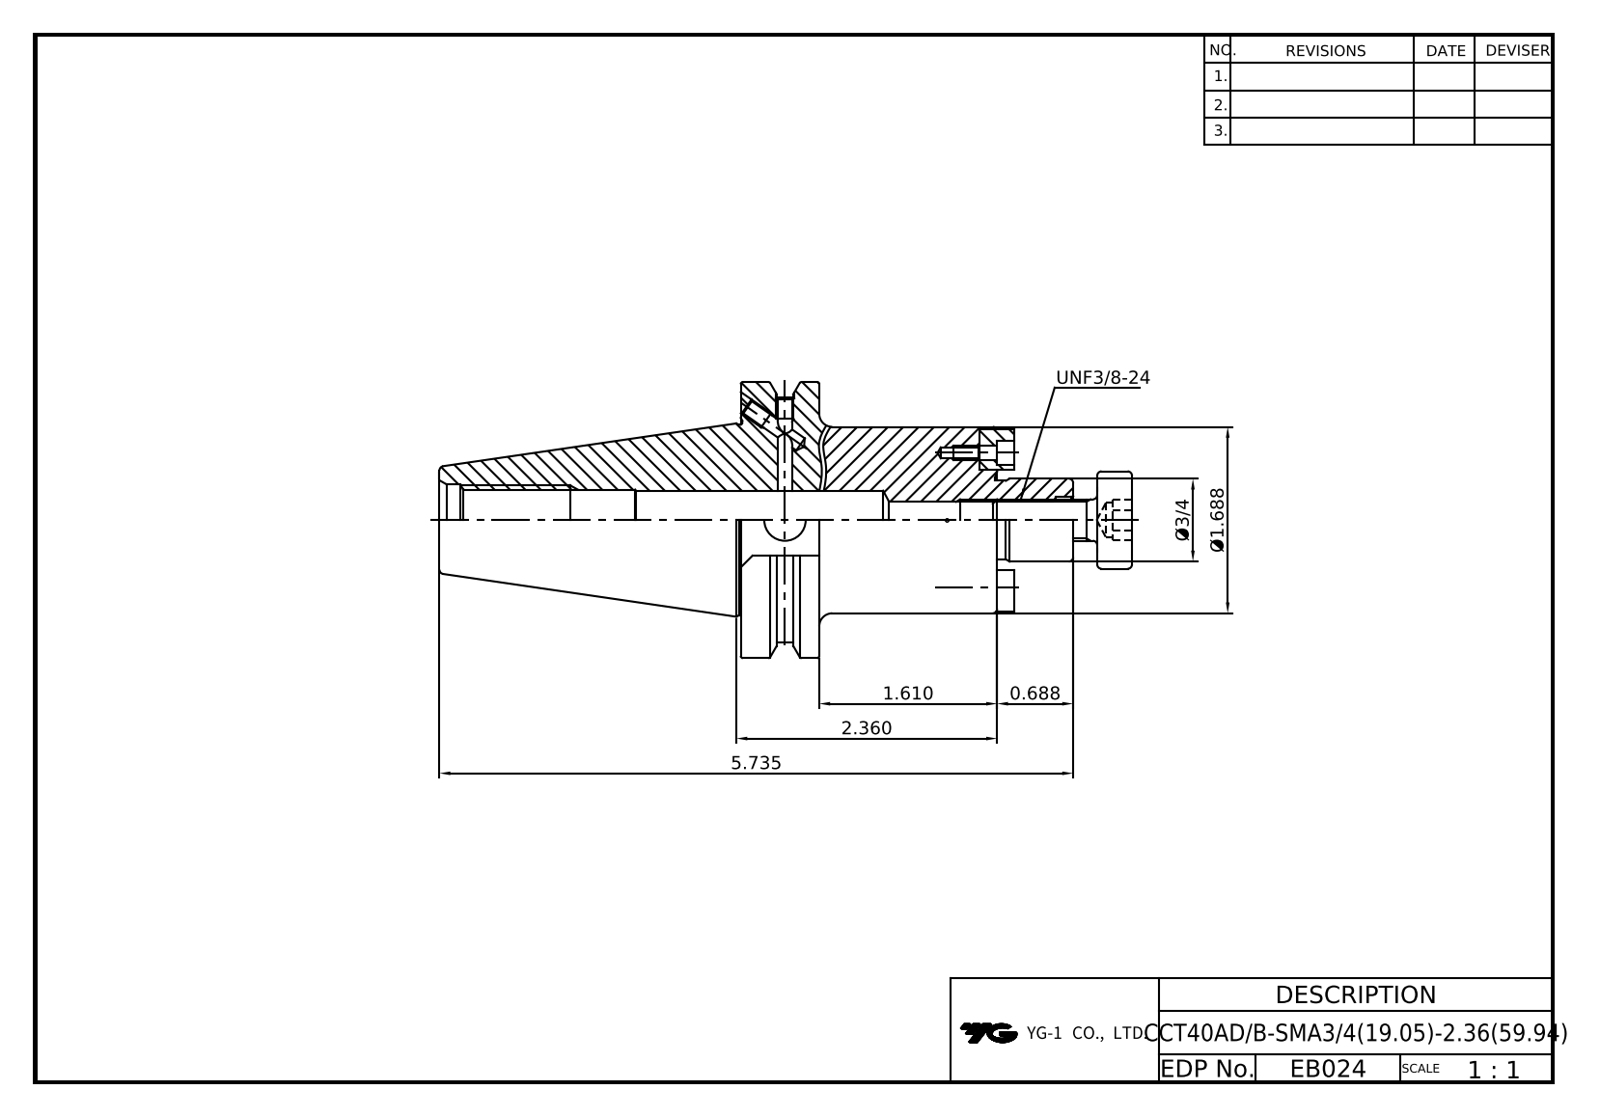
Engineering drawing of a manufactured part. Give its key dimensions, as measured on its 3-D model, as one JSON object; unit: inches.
{"part_name": "LO-CCT40ADB-SMA19.05-59.944; DRIVE KEY-7.93x7.93x9.5; HEX'' WRENCH BOLT-UNC#5-40x5_16L; COLLAR BOLT-UNF3_8-24x24L", "step_written_by": "Autodesk Inventor 2022 (AUTOMOTIVE_DESIGN)", "units": "inches", "bodies": {"solids": 6, "faces": 179, "planar": 90, "cylindrical": 47, "other": 42}, "overall_size": [6.247, 2.5, 2.405], "volume_in3": 10.27, "surface_area_in2": 50.9, "round_holes": [[0.128, 4], [0.098, 2], [0.13, 2], [0.157, 2], [0.165, 2], [0.213, 2], [0.313, 1], [0.33, 1], [0.375, 1], [0.413, 1], [0.512, 1], [0.527, 1]], "round_bosses_or_shafts": [[0.205, 2], [0.125, 2], [2.5, 1], [1.724, 1], [1.688, 1], [0.882, 1], [0.75, 1], [0.73, 1]], "partial_cylinders_radius": [[0.156, 2], [1.108, 1]], "face_to_face_distances": [0.711, 2.32, 1.61, 3.52, 2.81, 1.2, 2.164, 1.454, 0.156, 1.356], "hole_center_spacings": [0.609, 1.217]}
